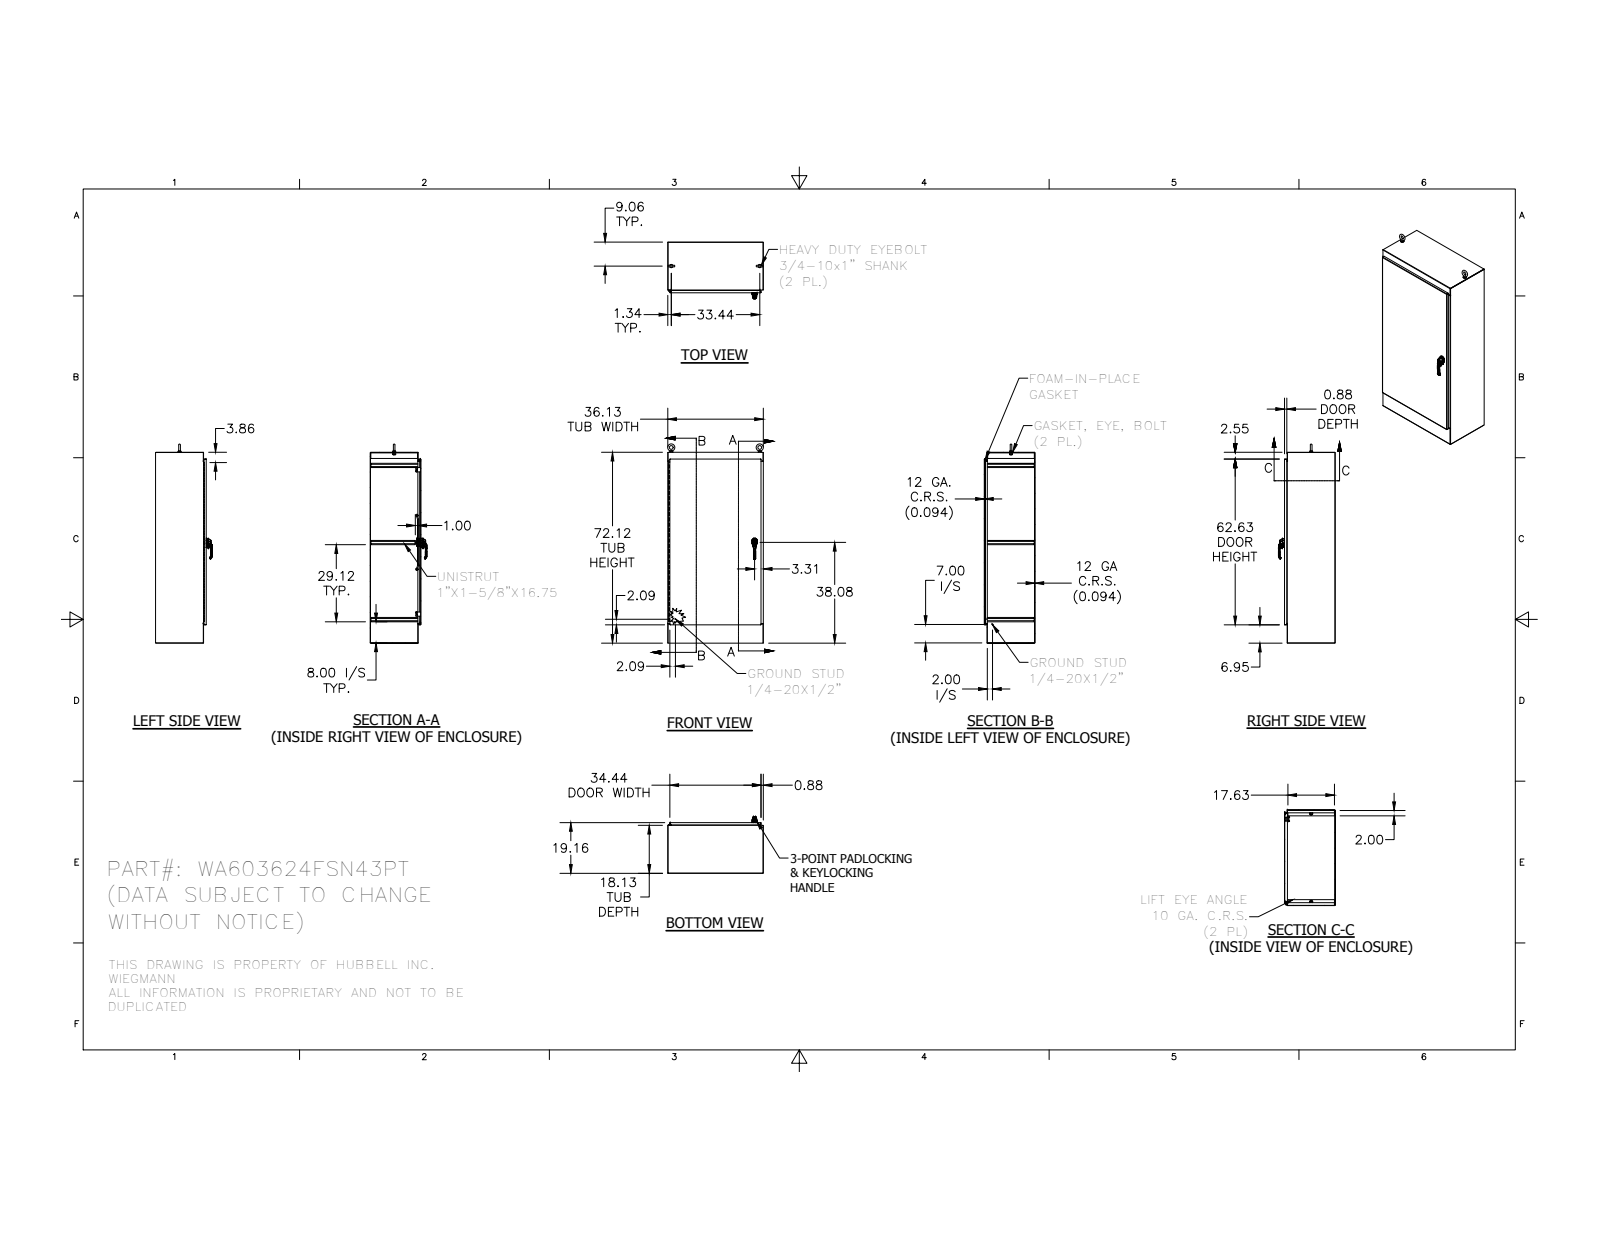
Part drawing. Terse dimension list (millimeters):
name: FUN00101; HFW31233; 316298; 7379-M6-8X25_AF0 (+8 more)
written by: SolidWorks 2014 (AUTOMOTIVE_DESIGN)
unit: mm
bodies: 52 solids, 1938 faces (834 planar, 782 cylindrical, 322 other)
size: 1911.3 × 917.6 × 486.7
volume: 16 880 000 mm³; area: 13 740 000 mm²
holes: 8× ⌀7, 4× ⌀5.1, 3× ⌀7.1, 2× ⌀6.1, 2× ⌀6.4, 2× ⌀6.4, 2× ⌀10.2, 2× ⌀10.3, 2× ⌀11.4, 2× ⌀16.3, 2× ⌀20.7, 1× ⌀3.2
bosses: 3× ⌀6.4, 2× ⌀31.8, 2× ⌀28.4, 2× ⌀25.4, 2× ⌀19.1, 2× ⌀14.3, 2× ⌀13.4, 2× ⌀12.7
rounds: 16× R0.3, 16× R0.8, 14× R1.3, 14× R3.2, 12× R0.5, 12× R1.3, 12× R2.2, 12× R3.2
face distances: 2.4, 484.3, 915.2, 481.9, 486.7, 912.8, 1829.6, 917.6, 458, 26.3
hole spacings: 1376.6, 1395.6, 19.4, 19.4, 30.4, 32.3, 1385.8, 1386.1
